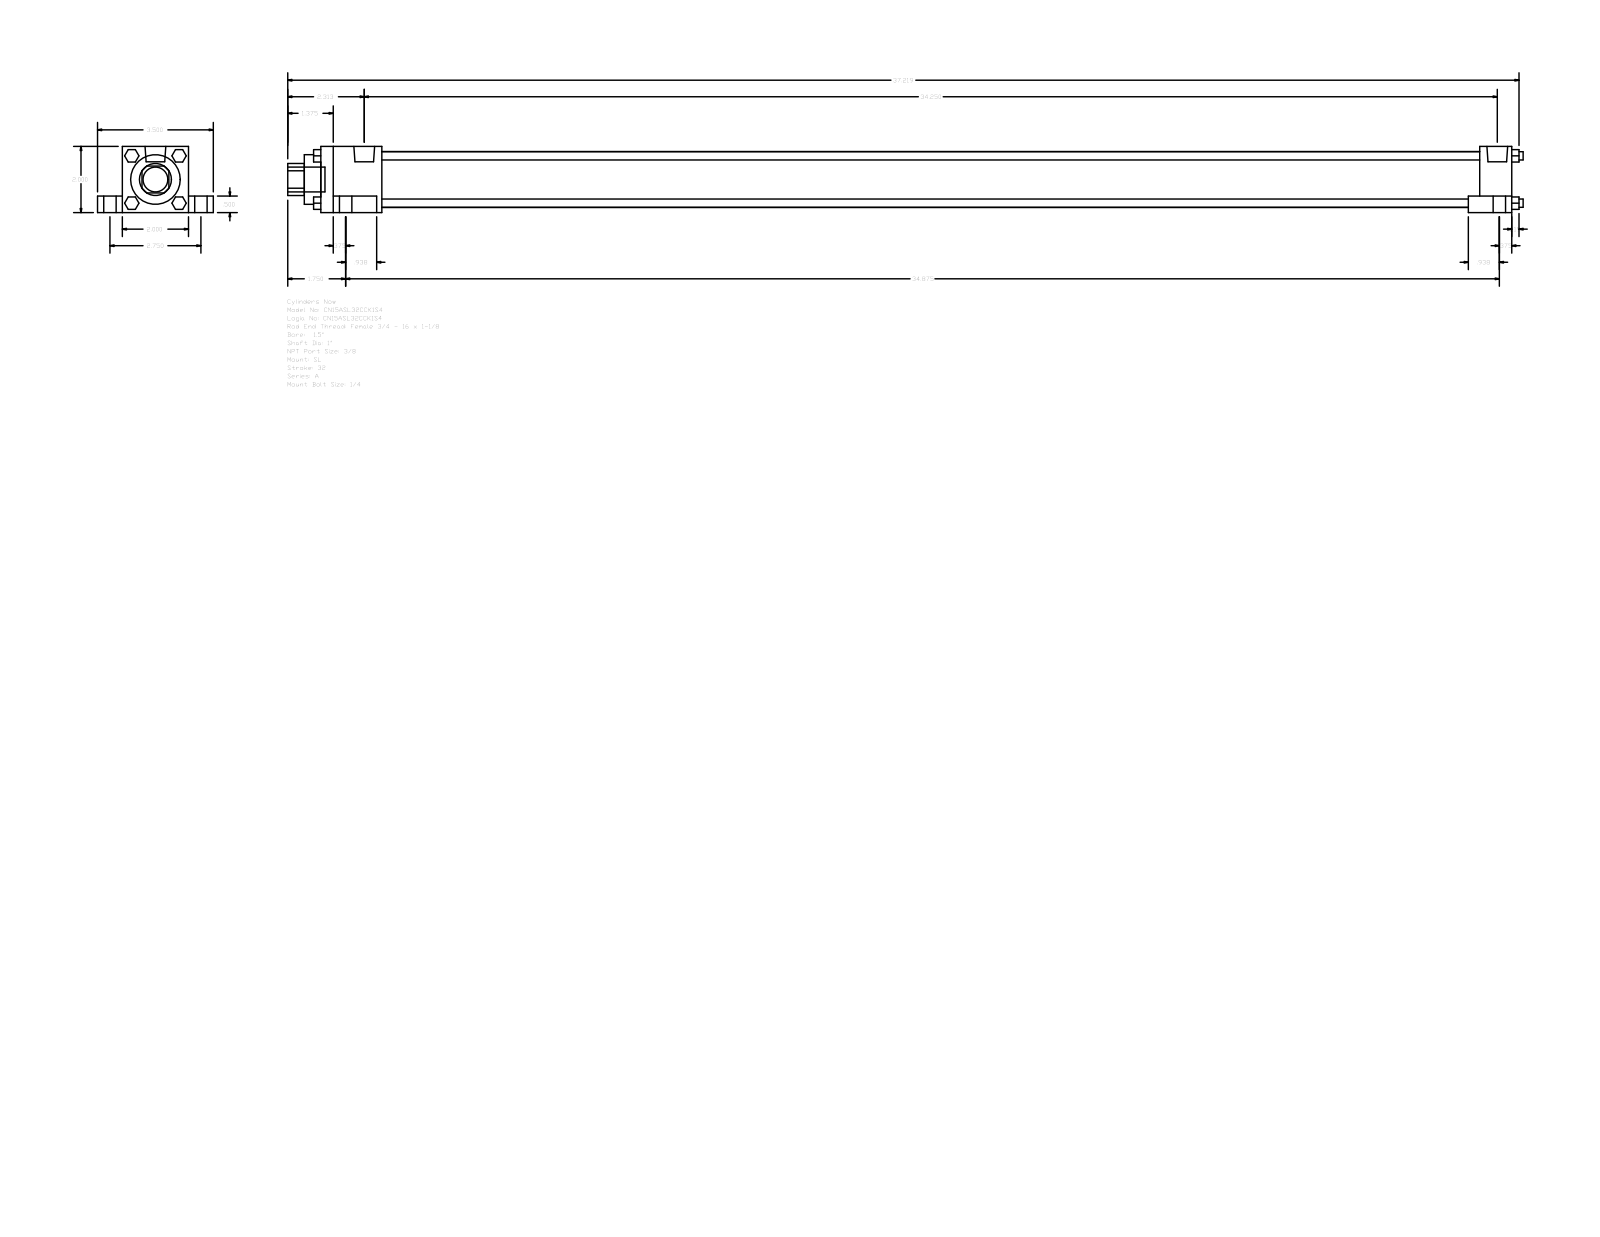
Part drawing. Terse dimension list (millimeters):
name: A_SL__0150_1
written by: GSSL Pune (CONFIG_CONTROL_DESIGN)
unit: mm
bodies: 0 solids, 148 faces (112 planar, 36 cylindrical, 0 other)
size: 948.53 × 88.9 × 50.8
holes: 1× ⌀25.4, 1× ⌀38.1, 1× ⌀42.93
bosses: 4× ⌀15.88, 4× ⌀9.53, 4× ⌀6.35, 4× ⌀5.56, 2× ⌀15.93, 1× ⌀19.05
rounds: 1× R12.29
face distances: 50.8, 12.7, 38.1, 19.05, 69.85, 9.52, 914.4, 33.34, 889.79, 24.61
